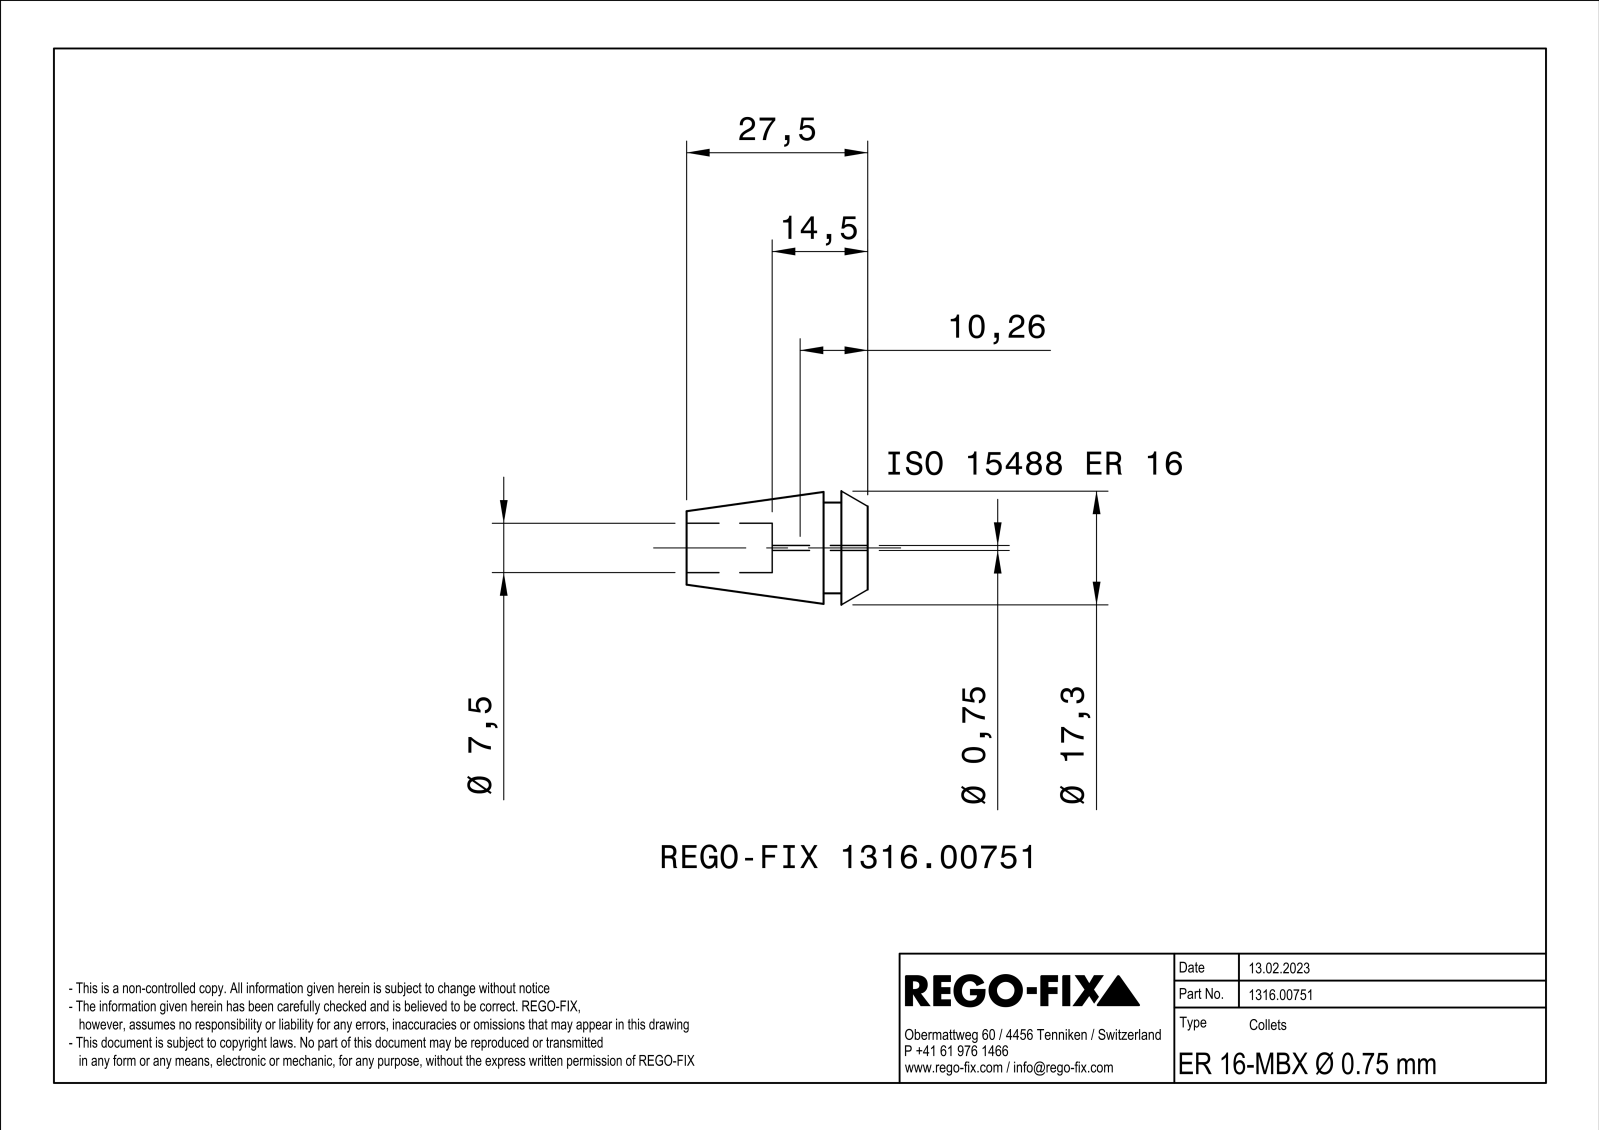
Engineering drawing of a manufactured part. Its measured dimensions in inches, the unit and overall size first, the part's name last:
Units: inches
Overall size (bounding box): 1.083 × 0.666 × 0.665
Round holes (diameter × count): ⌀0.079 ×3, ⌀0.295 ×1
Round bosses / shafts (diameter × count): ⌀0.543 ×1
Partial cylindrical surfaces — rounded edges, fillets, slot ends (radius × count): R0.006 ×3, R0.984 ×3, R0.015 ×1
Main face-to-face distances: 0.021, 0.031, 0.264, 0.157, 0.106, 1.083, 0.925, 0.819, 0.571, 0.413
Hole centre spacings: 0.083, 0.143
Volume: 0.202 in³ · Surface area: 5.143 in²
Bodies: 1 solid, 109 faces (36 planar, 27 cylindrical, 46 other)
Part name (STEP PRODUCT): NOCUT
STEP written by: SIEMENS PLM Software Solid Edge ST10 (AUTOMOTIVE_DESIGN)
